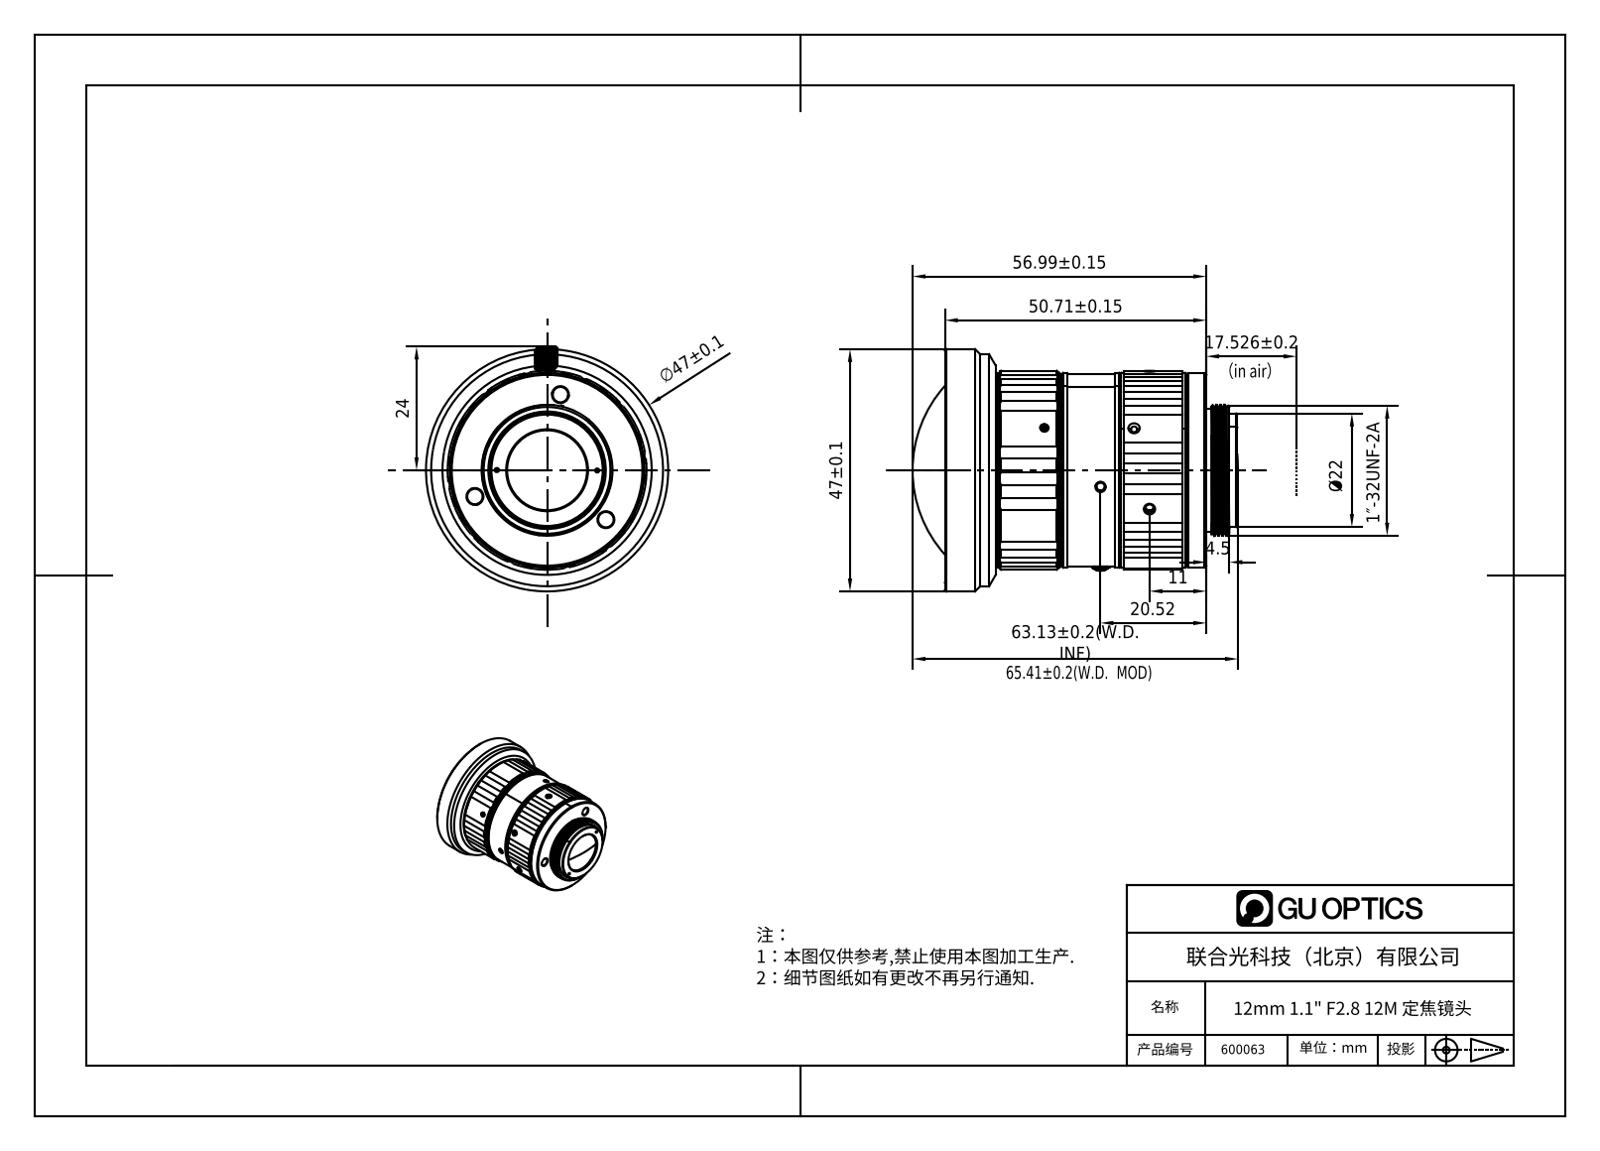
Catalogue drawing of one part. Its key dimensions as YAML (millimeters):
part_name: "600063"
step_written_by: "SolidWorks 2020 (CONFIG_CONTROL_DESIGN)"
units: millimeters
bodies: {solids: 10, faces: 1025, planar: 251, cylindrical: 412, other: 362}
overall_size: [63.13, 47, 47]
volume: 67841
surface_area: 21952
round_holes:
  - {diameter: 1.6, count: 6}
  - {diameter: 1.2, count: 3}
  - {diameter: 0.8, count: 2}
  - {diameter: 15.5, count: 1}
  - {diameter: 19.46, count: 1}
  - {diameter: 20.4, count: 1}
  - {diameter: 22.2, count: 1}
  - {diameter: 36.2, count: 1}
  - {diameter: 36.7, count: 1}
  - {diameter: 40.9, count: 1}
  - {diameter: 41.5, count: 1}
  - {diameter: 43.5, count: 1}
round_bosses_or_shafts:
  - {diameter: 1.6, count: 5}
  - {diameter: 2.5, count: 3}
  - {diameter: 2, count: 2}
  - {diameter: 47, count: 1}
  - {diameter: 45, count: 1}
  - {diameter: 44, count: 1}
  - {diameter: 39.8, count: 1}
  - {diameter: 38.6, count: 1}
partial_cylinders:
  - {radius: 2, count: 26}
  - {radius: 3, count: 18}
  - {radius: 0.3, count: 2}
face_to_face_distances: [3, 45.76, 42.76, 1.52, 45.6, 42.6, 1.9, 4.52, 47.12, 47.28]
hole_center_spacings: [9.73, 19.46]
